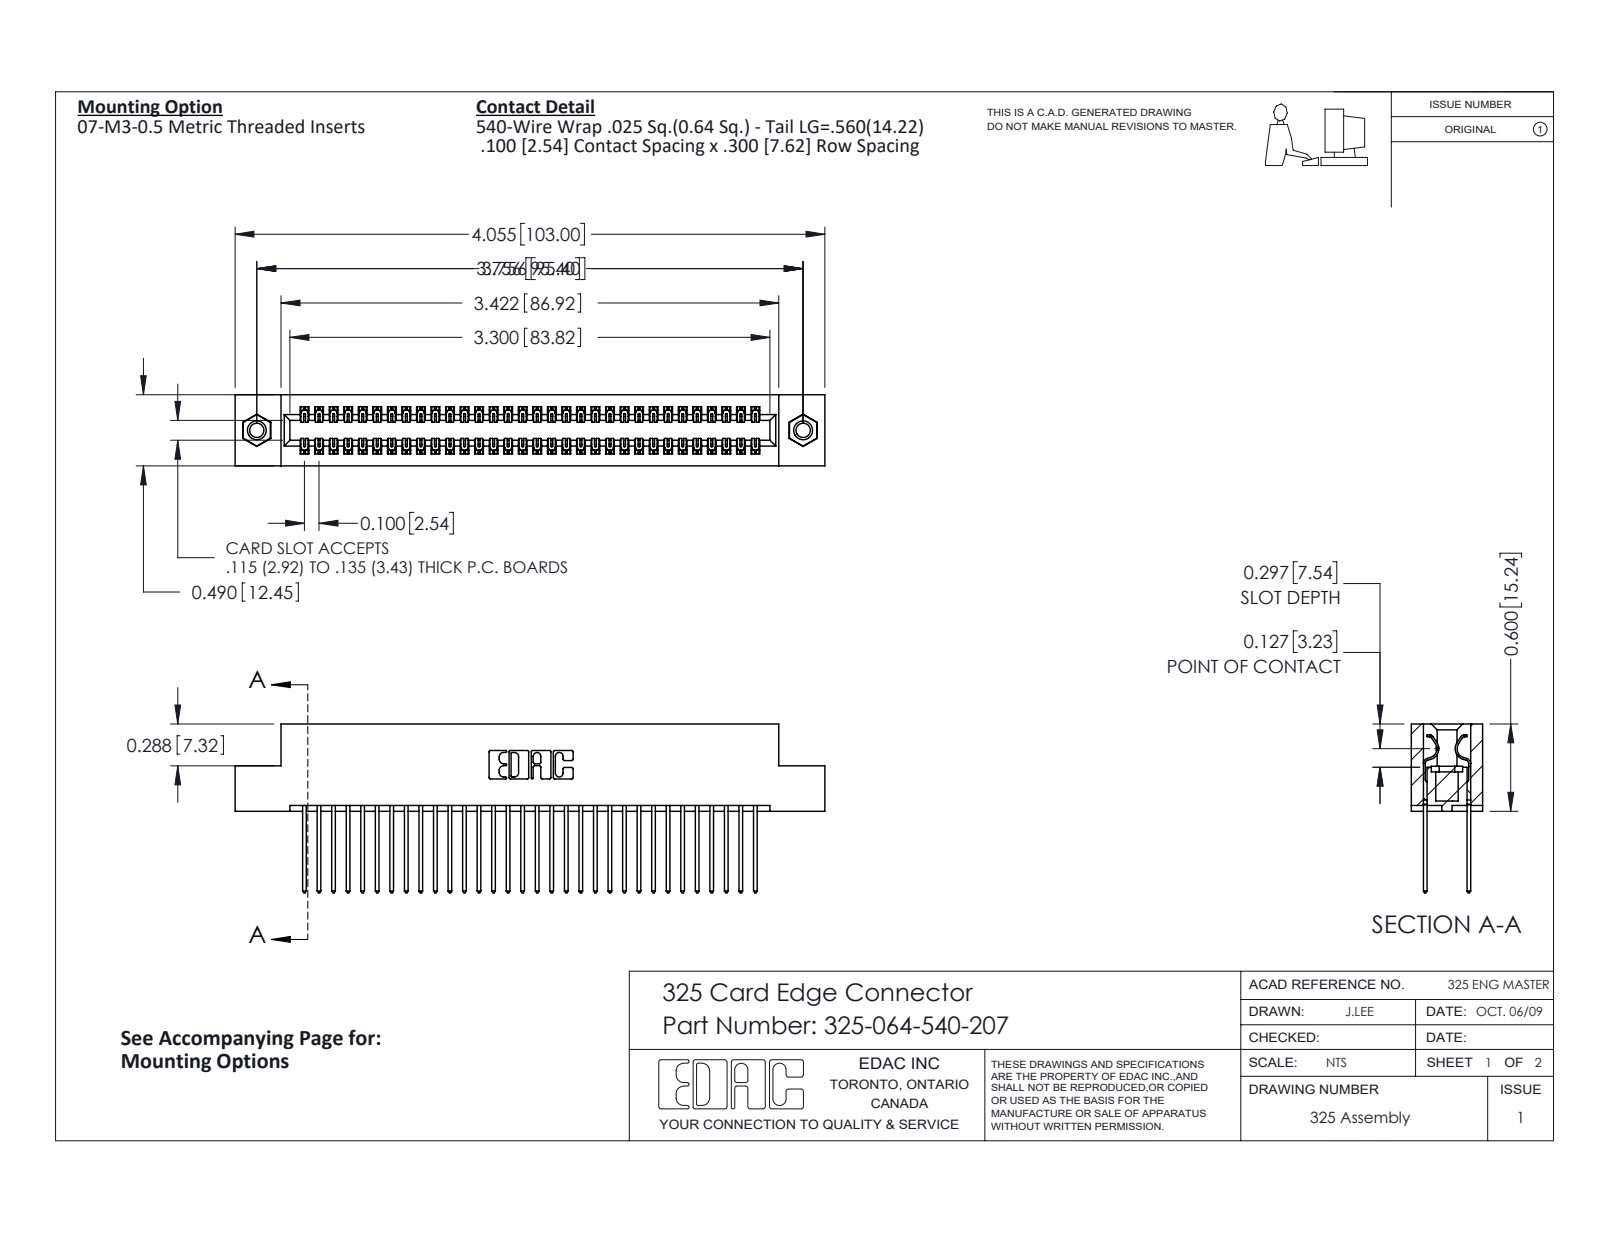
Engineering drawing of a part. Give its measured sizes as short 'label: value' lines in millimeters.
name: 325-292-001_325-293-140; 325 Part_TI; 325-064-540-207; 345-250-001_345-250-005-103
written by: SolidWorks 2016 (CONFIG_CONTROL_DESIGN)
unit: mm
bodies: 67 solids, 3502 faces (2406 planar, 1080 cylindrical, 16 other)
size: 103 × 29.5 × 12.4
volume: 13 400 mm³; area: 17 210 mm²
holes: 2× ⌀2.5, 2× ⌀3.2, 2× ⌀4.1
bosses: 2× ⌀3.9
rounds: 96× R0.2, 64× R0.3, 22× R0.3, 6× R0.2, 6× R0.8, 3× R0.7, 2× R0.4, 2× R0.6
face distances: 2.1, 10.3, 7.6, 2.7, 9.7, 0.6, 12.4, 8.3, 7, 1
hole spacings: 95.4
